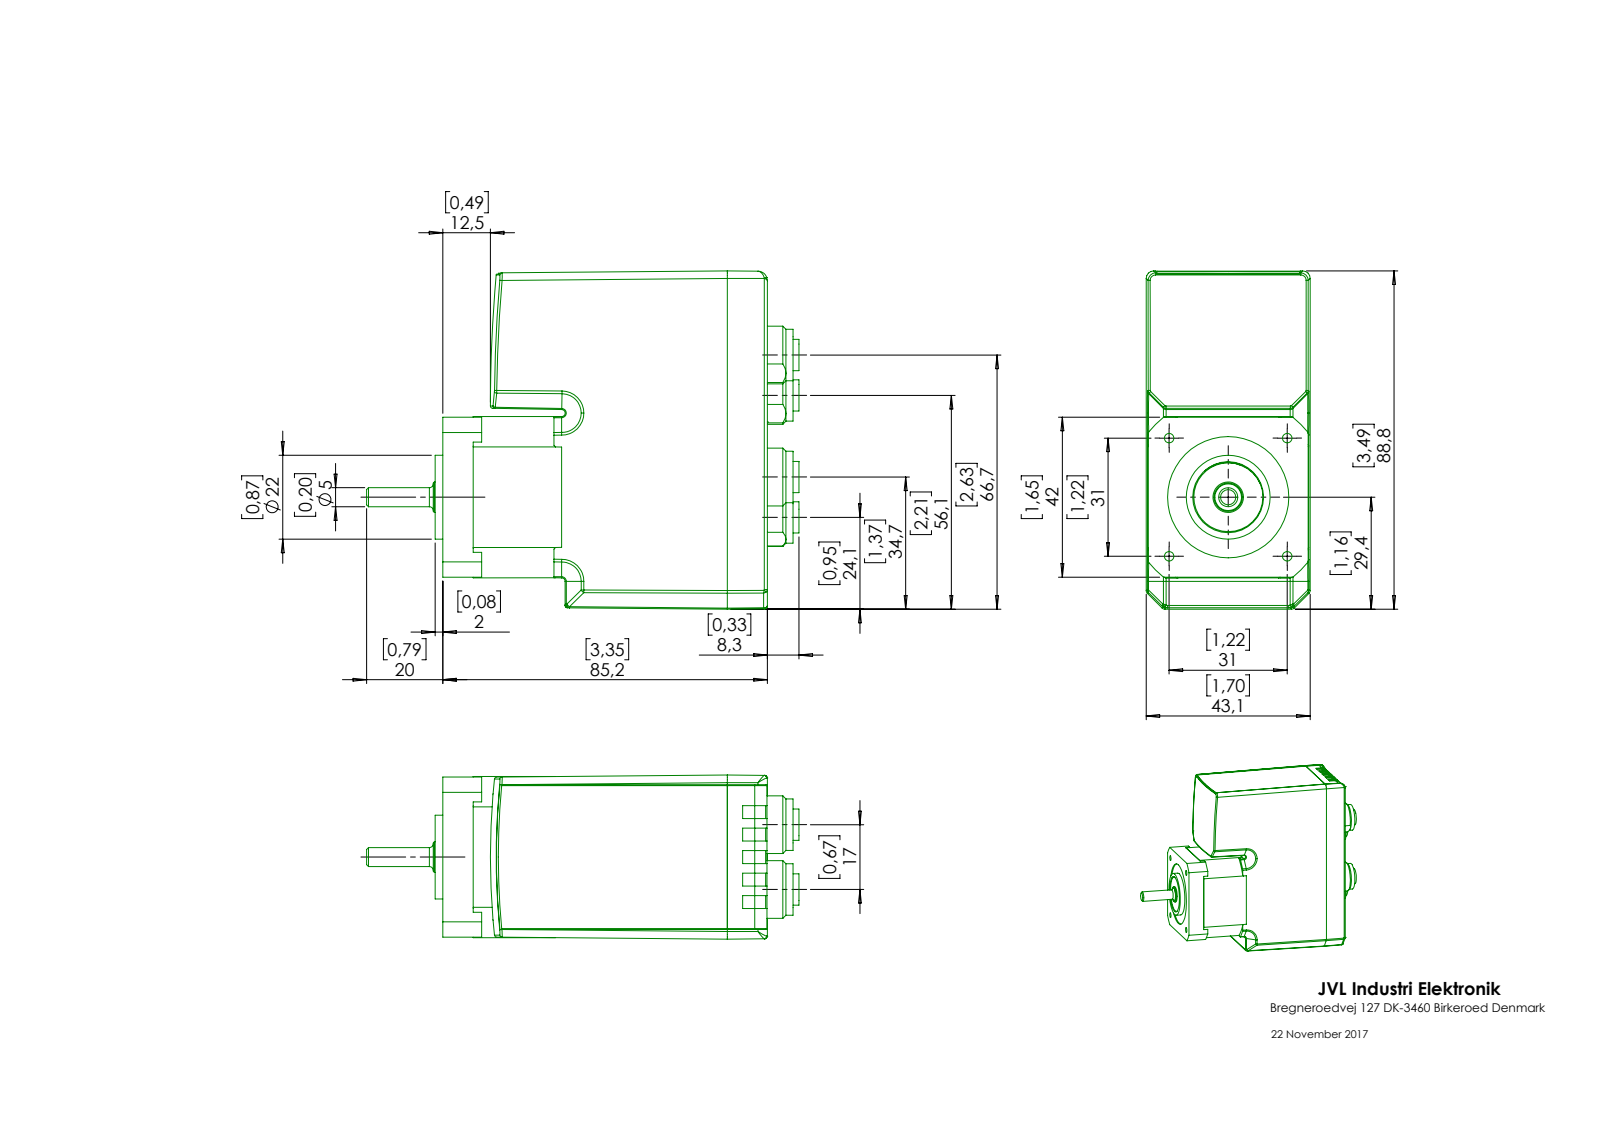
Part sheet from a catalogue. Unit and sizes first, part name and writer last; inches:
Units: inches
Overall size (bounding box): 4.469 × 3.494 × 1.695
Round holes (diameter × count): ⌀0.059 ×5, ⌀0.098 ×4, ⌀0.472 ×4, ⌀0.13 ×1, ⌀0.327 ×1, ⌀1.252 ×1
Round bosses / shafts (diameter × count): ⌀0.596 ×4, ⌀0.531 ×4, ⌀0.323 ×4, ⌀0.866 ×1, ⌀0.315 ×1, ⌀0.295 ×1, ⌀0.197 ×1
Partial cylindrical surfaces — rounded edges, fillets, slot ends (radius × count): R0.039 ×30, R0.031 ×3, R0.037 ×2, R0.079 ×2, R0.15 ×2, R0.165 ×2, R0.014 ×1, R0.024 ×1
Main face-to-face distances: 1.696, 1.665, 1.659, 3.35, 3.354, 1.654, 0.02, 3.331, 3.335, 0.014
Hole centre spacings: 0.198, 0.754, 0.863, 1.024, 1.22, 1.256, 1.26, 1.608
Volume: 17.37 in³ · Surface area: 51.71 in²
Bodies: 1 solid, 447 faces (181 planar, 150 cylindrical, 116 other)
Part name (STEP PRODUCT): MIS173 M12 END Ø5
STEP written by: SolidWorks 2017 (CONFIG_CONTROL_DESIGN)
